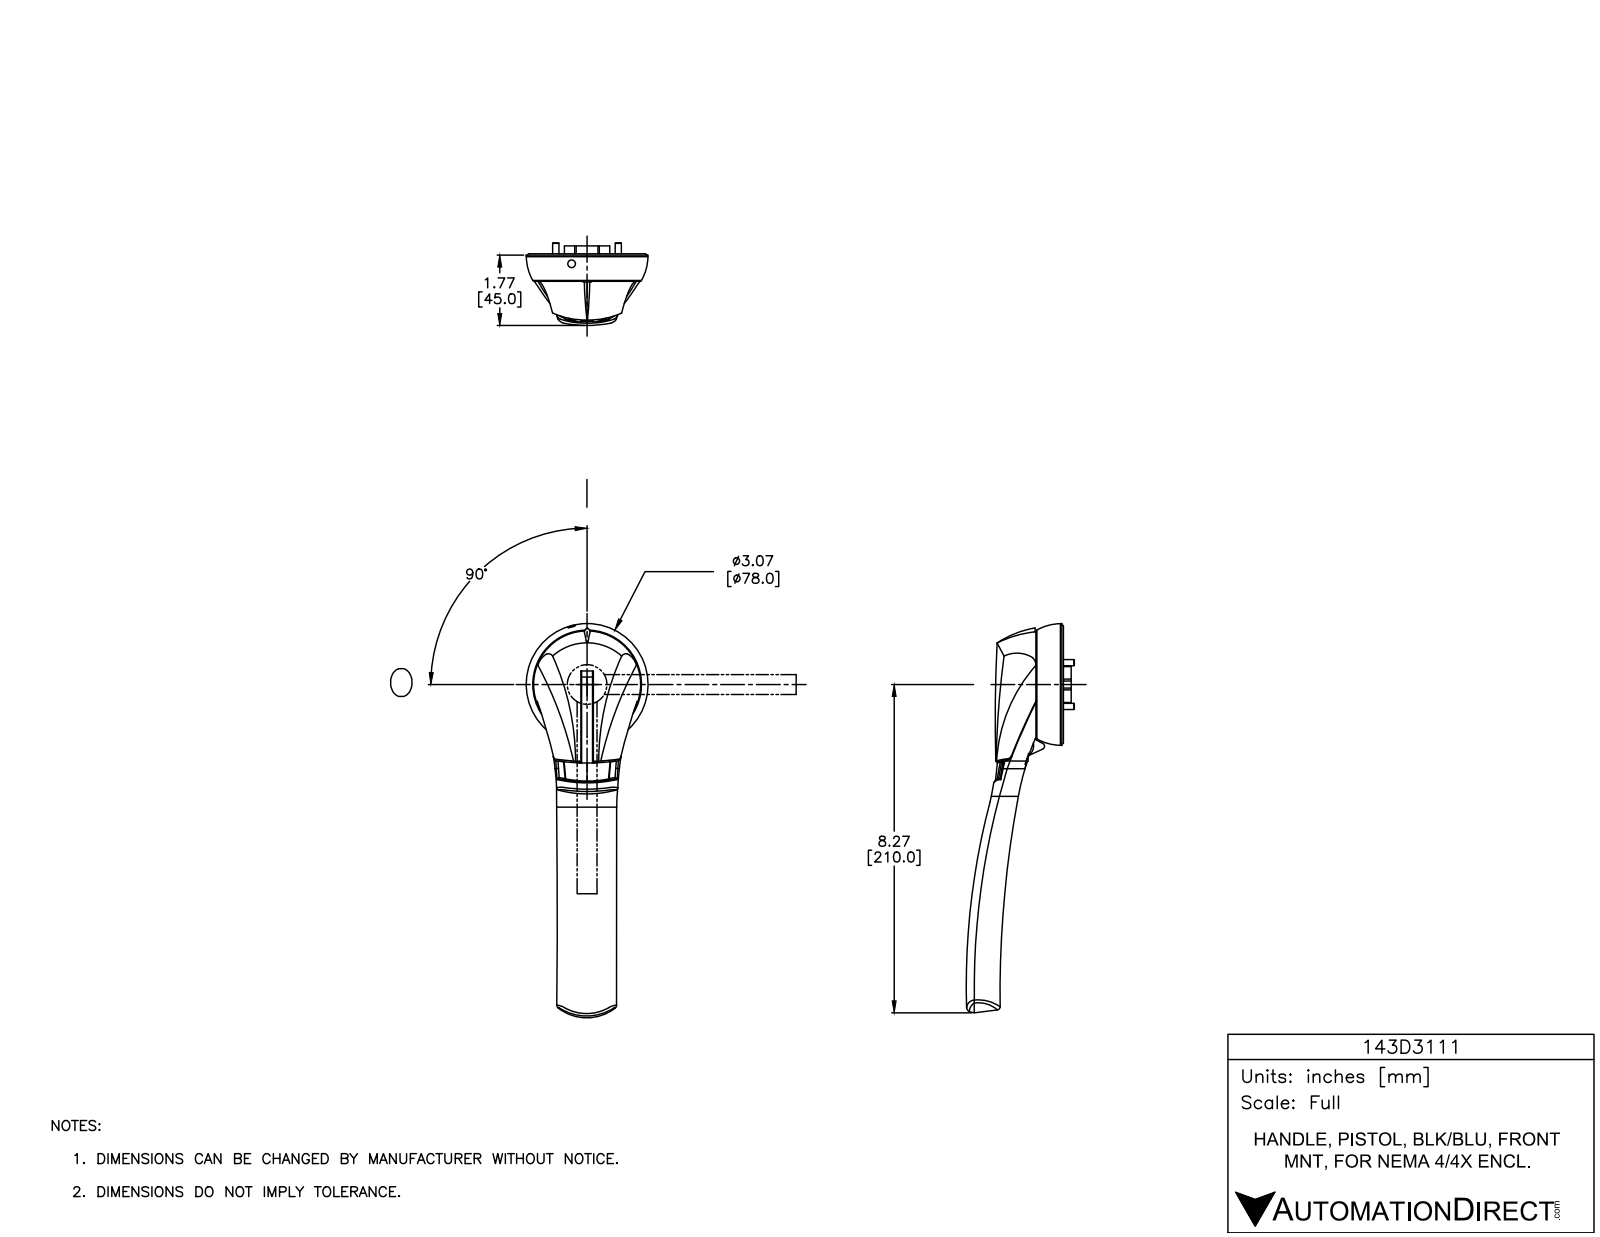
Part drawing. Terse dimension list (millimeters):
name: 143D3111
written by: SolidWorks 2015 (AUTOMOTIVE_DESIGN)
unit: mm
bodies: 8 solids, 1514 faces (806 planar, 544 cylindrical, 164 other)
size: 248.7 × 78 × 69.1
volume: 211 600 mm³; area: 64 770 mm²
holes: 6× ⌀4, 4× ⌀8.6, 4× ⌀10.8, 3× ⌀0.8, 2× ⌀4.3, 2× ⌀9.2, 1× ⌀3, 1× ⌀4.8, 1× ⌀76
bosses: 11× ⌀0.5, 4× ⌀8.5, 4× ⌀8, 3× ⌀2.3, 3× ⌀1.8, 2× ⌀5.8, 1× ⌀71.6, 1× ⌀68.6
rounds: 221× R0.3, 20× R0.4, 20× R0.9, 15× R0.8, 4× R1, 3× R0.6, 3× R138.1, 2× R2
face distances: 0.6, 17.8, 18.1, 17.5, 0.9, 7, 2.6, 4.4, 6.2, 1.2
hole spacings: 24.4, 7.8, 17, 27.9, 28, 30.6, 40, 47.8
